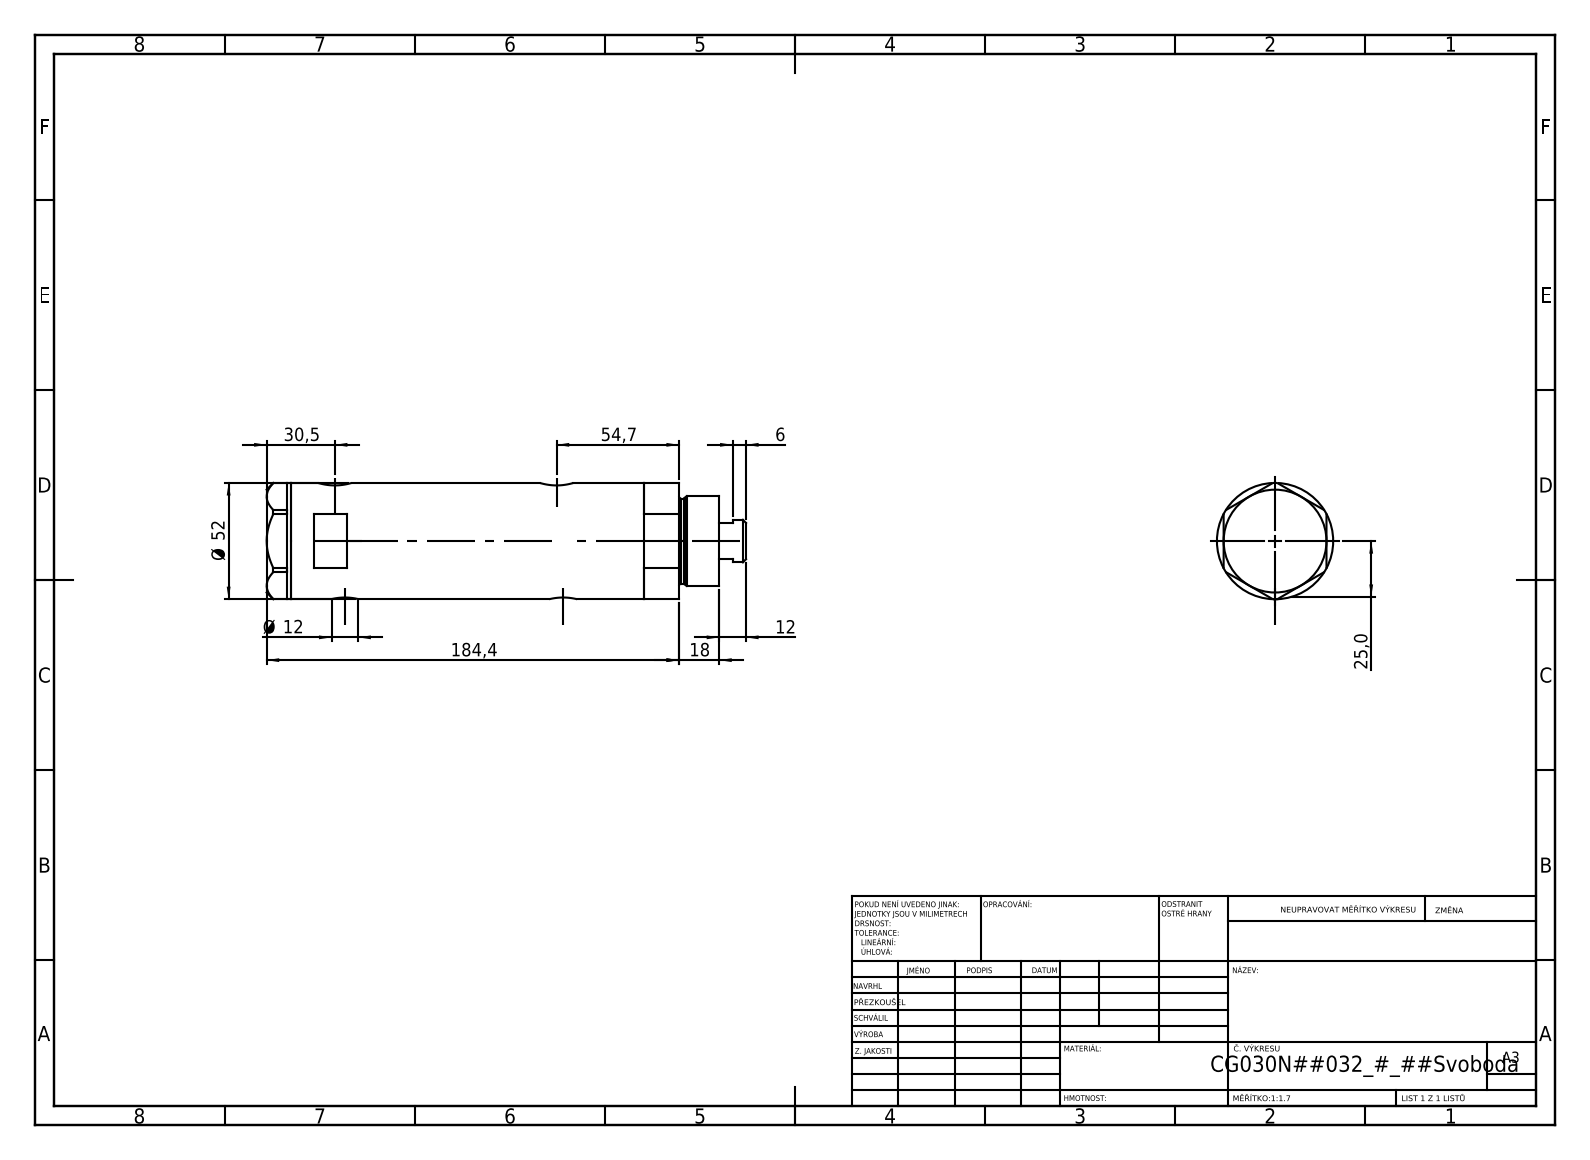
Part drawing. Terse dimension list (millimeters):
name: V270CG_FRONT; V270CG_BACK; V270CG_VC; V270CG_MIDDLE
written by: SolidWorks 2019 (CONFIG_CONTROL_DESIGN)
unit: mm
bodies: 4 solids, 140 faces (67 planar, 53 cylindrical, 20 other)
size: 214.4 × 52 × 52
volume: 395 637 mm³; area: 87 123 mm²
holes: 2× ⌀5, 2× ⌀9.73, 2× ⌀12.5, 2× ⌀15, 1× ⌀6.5, 1× ⌀20, 1× ⌀21.5, 1× ⌀30, 1× ⌀33, 1× ⌀44
bosses: 2× ⌀12, 1× ⌀52, 1× ⌀40, 1× ⌀38, 1× ⌀19
face distances: 121.5, 23.8, 97.7, 11, 34.8, 132.5, 46, 168.9, 157.9, 134.1
hole spacings: 2.9, 4.5, 94.7, 97.6, 99.2, 102.1
